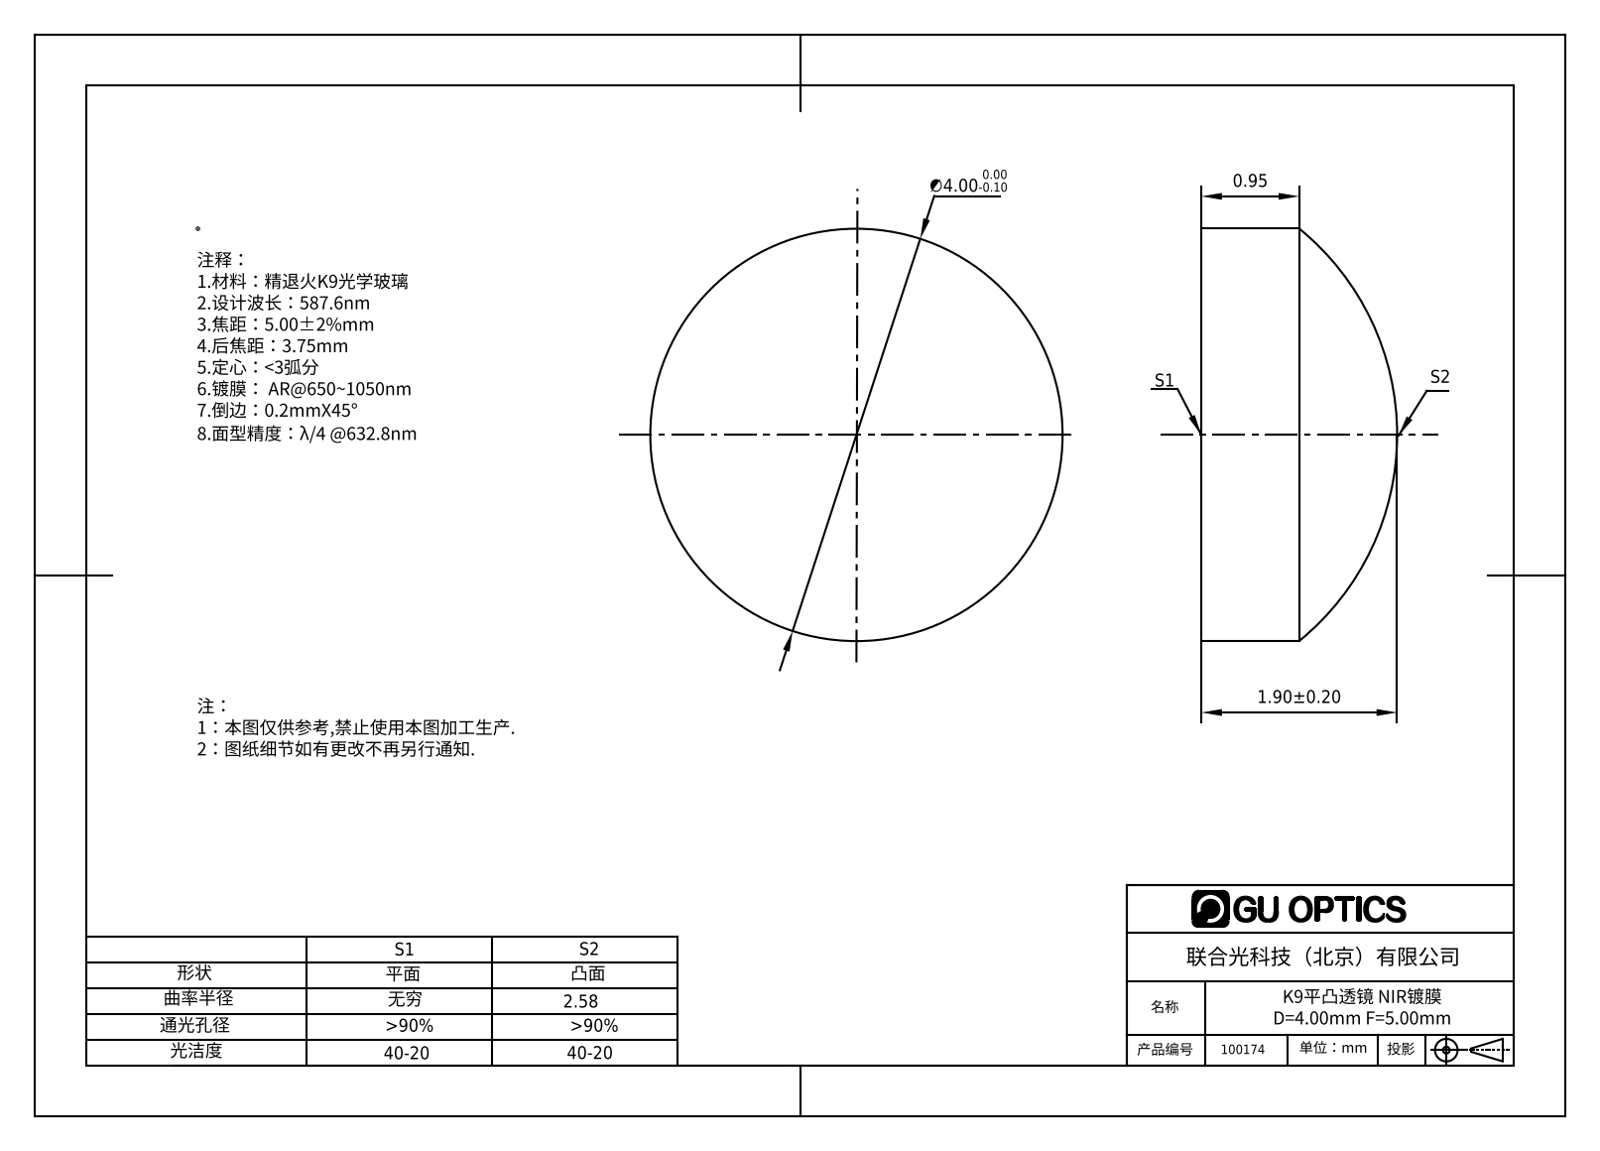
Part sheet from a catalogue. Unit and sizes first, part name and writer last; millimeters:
Units: millimetres
Overall size (bounding box): 4 × 4 × 1.9
Round bosses / shafts (diameter × count): ⌀4 ×1
Volume: 18 mm³ · Surface area: 40 mm²
Bodies: 1 solid, 5 faces (1 planar, 2 cylindrical, 2 other)
Part name (STEP PRODUCT): 100174
STEP written by: SolidWorks 2016 (AUTOMOTIVE_DESIGN)
